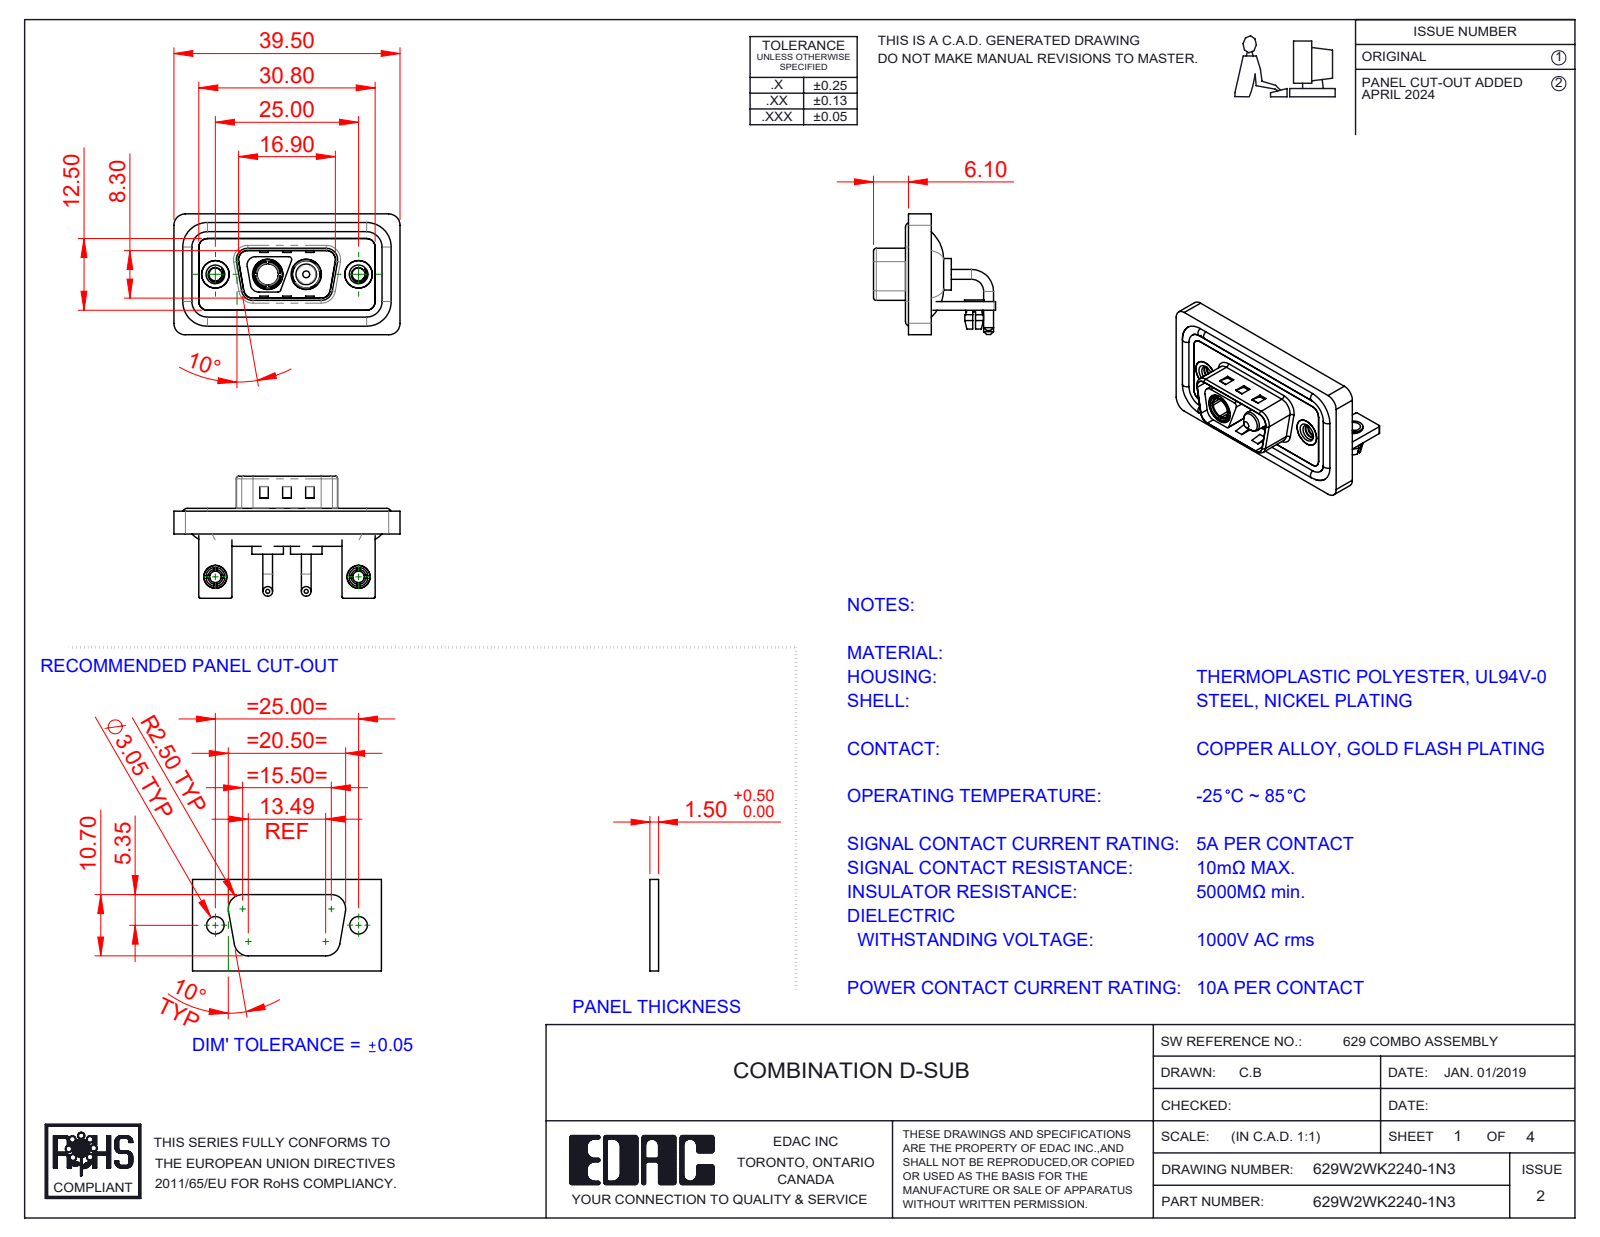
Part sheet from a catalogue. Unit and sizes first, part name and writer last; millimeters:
Units: millimetres
Overall size (bounding box): 39.5 × 21.3 × 21.1
Round holes (diameter × count): ⌀2 ×2, ⌀2.26 ×2, ⌀2.5 ×2, ⌀3.2 ×2, ⌀4 ×2, ⌀4.8 ×2, ⌀4.85 ×2, ⌀5 ×2, ⌀5.3 ×2, ⌀3.7 ×1
Round bosses / shafts (diameter × count): ⌀1.7 ×4, ⌀1.6 ×4, ⌀5.5 ×2, ⌀5.2 ×2, ⌀4.9 ×2, ⌀4.75 ×2, ⌀4 ×2, ⌀3.75 ×2
Partial cylindrical surfaces — rounded edges, fillets, slot ends (radius × count): R1.5 ×20, R2 ×19, R0.25 ×16, R0.5 ×11, R1.6 ×8, R0.6 ×4, R0.65 ×4, R0.9 ×4
Main face-to-face distances: 0.4, 1.5, 2.9, 0.8, 1.1, 1.2, 2.1, 1.6, 3.7, 2.5
Hole centre spacings: 9.14, 15.86, 25, 6.72
Volume: 4 877 mm³ · Surface area: 8 225 mm²
Bodies: 15 solids, 674 faces (257 planar, 281 cylindrical, 136 other)
Part name (STEP PRODUCT): 629Combo Shell Rear_09 Contacts; 629Combo Stabilizer Bracket; Power Socket_10A RA; 629Combo Housing_2WK2 (+6 more)
STEP written by: SolidWorks 2023 (CONFIG_CONTROL_DESIGN)
